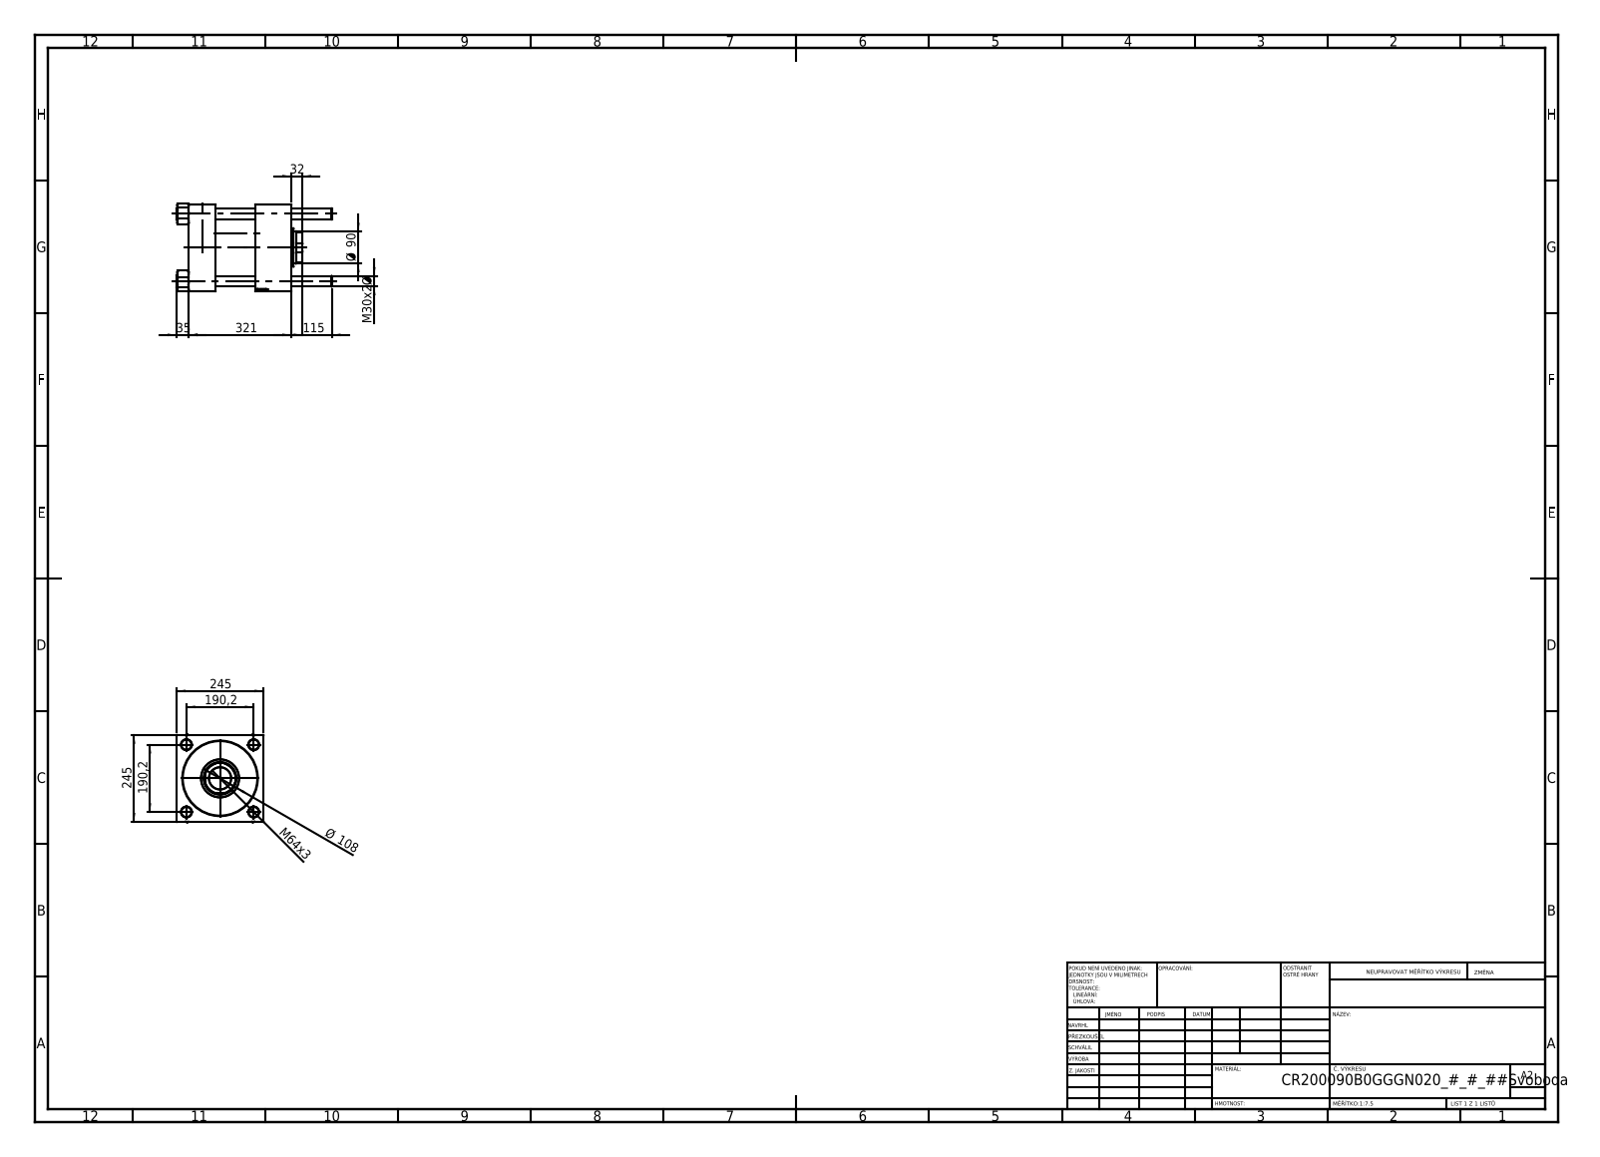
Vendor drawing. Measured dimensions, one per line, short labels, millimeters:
name: V215CR_VCP_B; V215CR_B-1; V215CR_B_TYCINKA; V215_VC_A (+1 more)
written by: SolidWorks 2019 (CONFIG_CONTROL_DESIGN)
unit: mm
bodies: 11 solids, 1206 faces (479 planar, 79 cylindrical, 648 other)
size: 439 × 249.22 × 245
volume: 13 930 000 mm³; area: 1 125 000 mm²
holes: 4× ⌀30, 2× ⌀7, 2× ⌀41.92, 1× ⌀35, 1× ⌀52, 1× ⌀62.5, 1× ⌀90, 1× ⌀93, 1× ⌀146, 1× ⌀200, 1× ⌀210.5
bosses: 4× ⌀33, 1× ⌀206, 1× ⌀108
rounds: 1× R44
face distances: 245, 76, 289, 213, 260.3, 184.3, 28.7, 101, 188, 112
hole spacings: 134.49, 190.2, 268.98, 191.92
